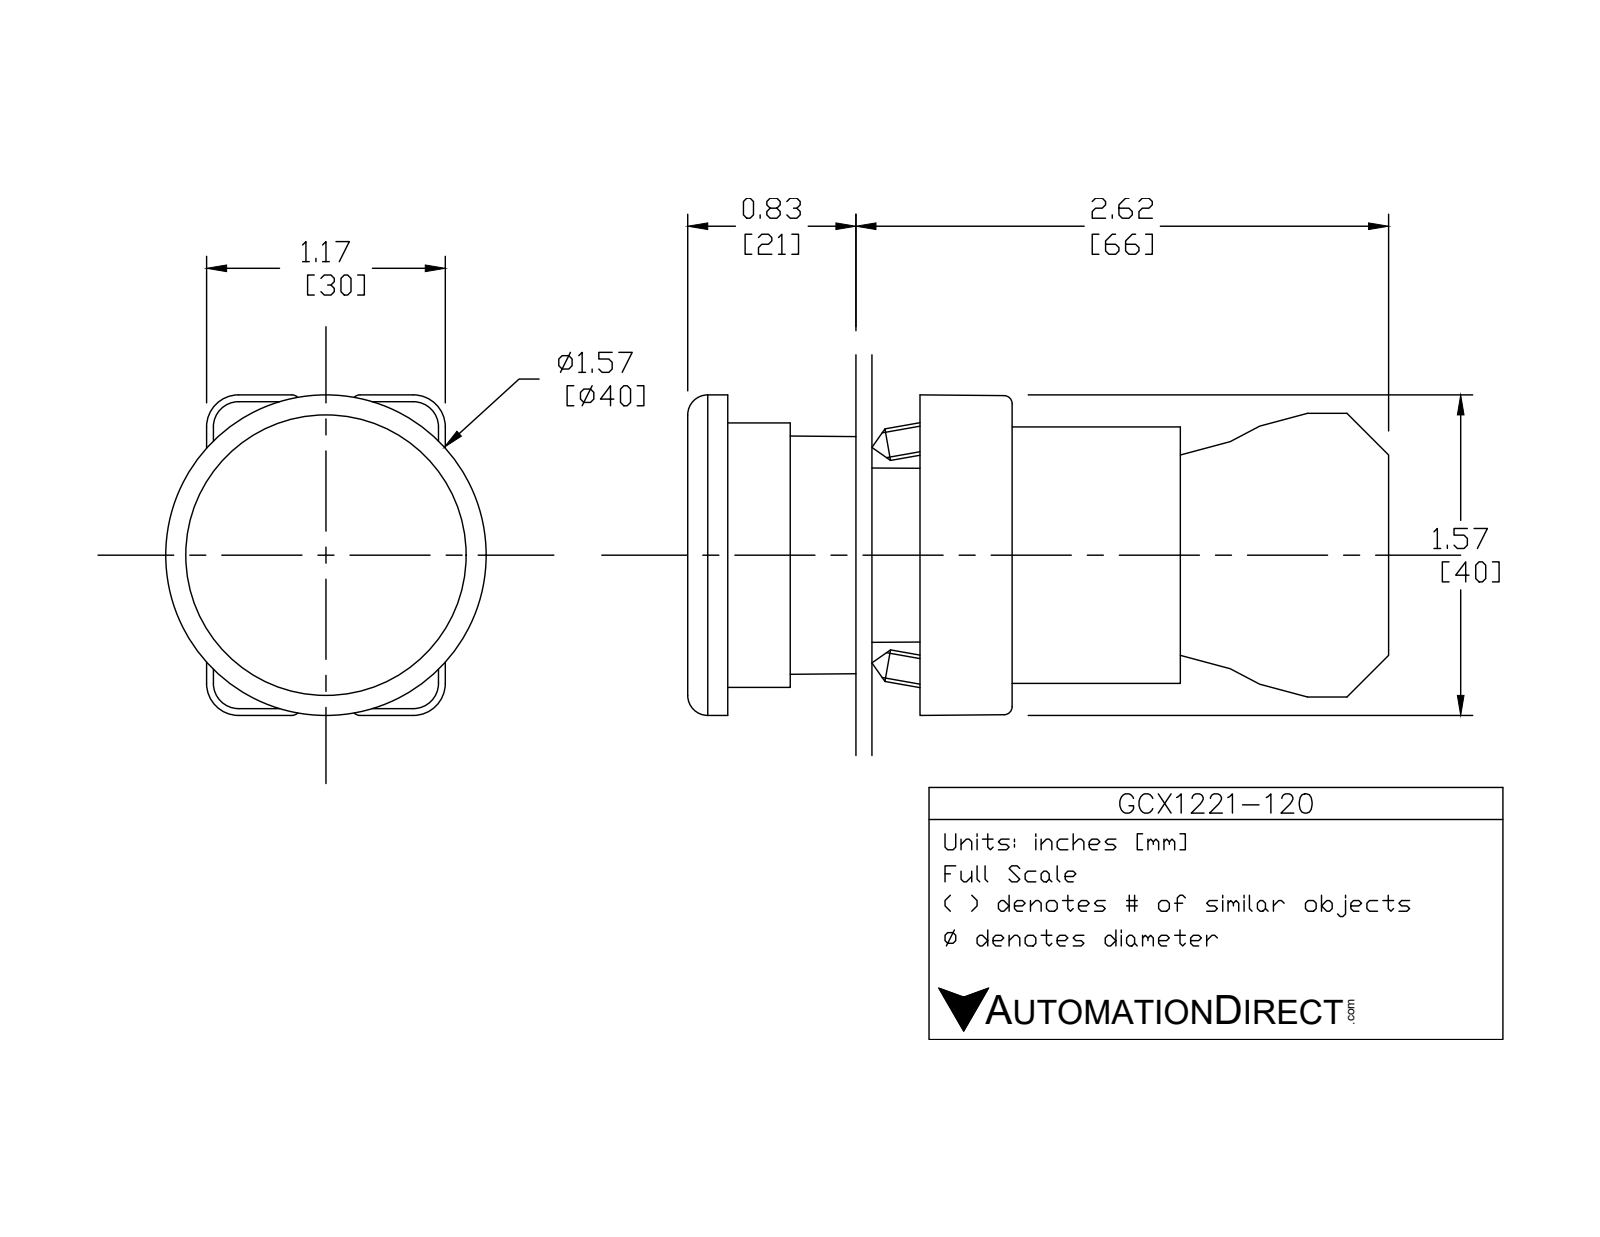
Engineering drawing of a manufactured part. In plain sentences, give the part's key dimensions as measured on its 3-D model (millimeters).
The part is named "ECX1029-2; ecx1030; GCX1221-120; ECX1050 (+1 more)". Its 3-D file was written by "SolidWorks 2016 (AUTOMOTIVE_DESIGN)". It is 7 solids with 431 faces: 252 planar, 146 cylindrical and 33 other. Overall it measures 88.1 by 40.2 by 40 millimeters. Its volume is 47 440 cubic millimeters and its surface area 26 380 square millimeters. Round holes: 2 of diameter 2, 2 of diameter 3.1, 2 of diameter 3.3, 1 of diameter 2.2, 1 of diameter 5, 1 of diameter 11.9, 1 of diameter 22.3, 1 of diameter 22.6, 1 of diameter 26, 1 of diameter 30. Round bosses or shafts: 4 of diameter 4, 1 of diameter 33, 1 of diameter 29.8, 1 of diameter 24, 1 of diameter 21.7, 1 of diameter 19.8, 1 of diameter 12.8. Partial cylindrical surfaces (rounded edges, fillets, slot ends): 24 of radius 1.5, 12 of radius 1, 12 of radius 3.1, 12 of radius 4, 8 of radius 1, 2 of radius 3.3, 1 of radius 0.5, 1 of radius 1.6. The main face-to-face distances are 21, 62.1, 41.1, 14.7, 58.1, 37.1, 4, 14.9, 0.8, 29.6. The hole center spacings are 6, 13.7, 12, 12.3.
